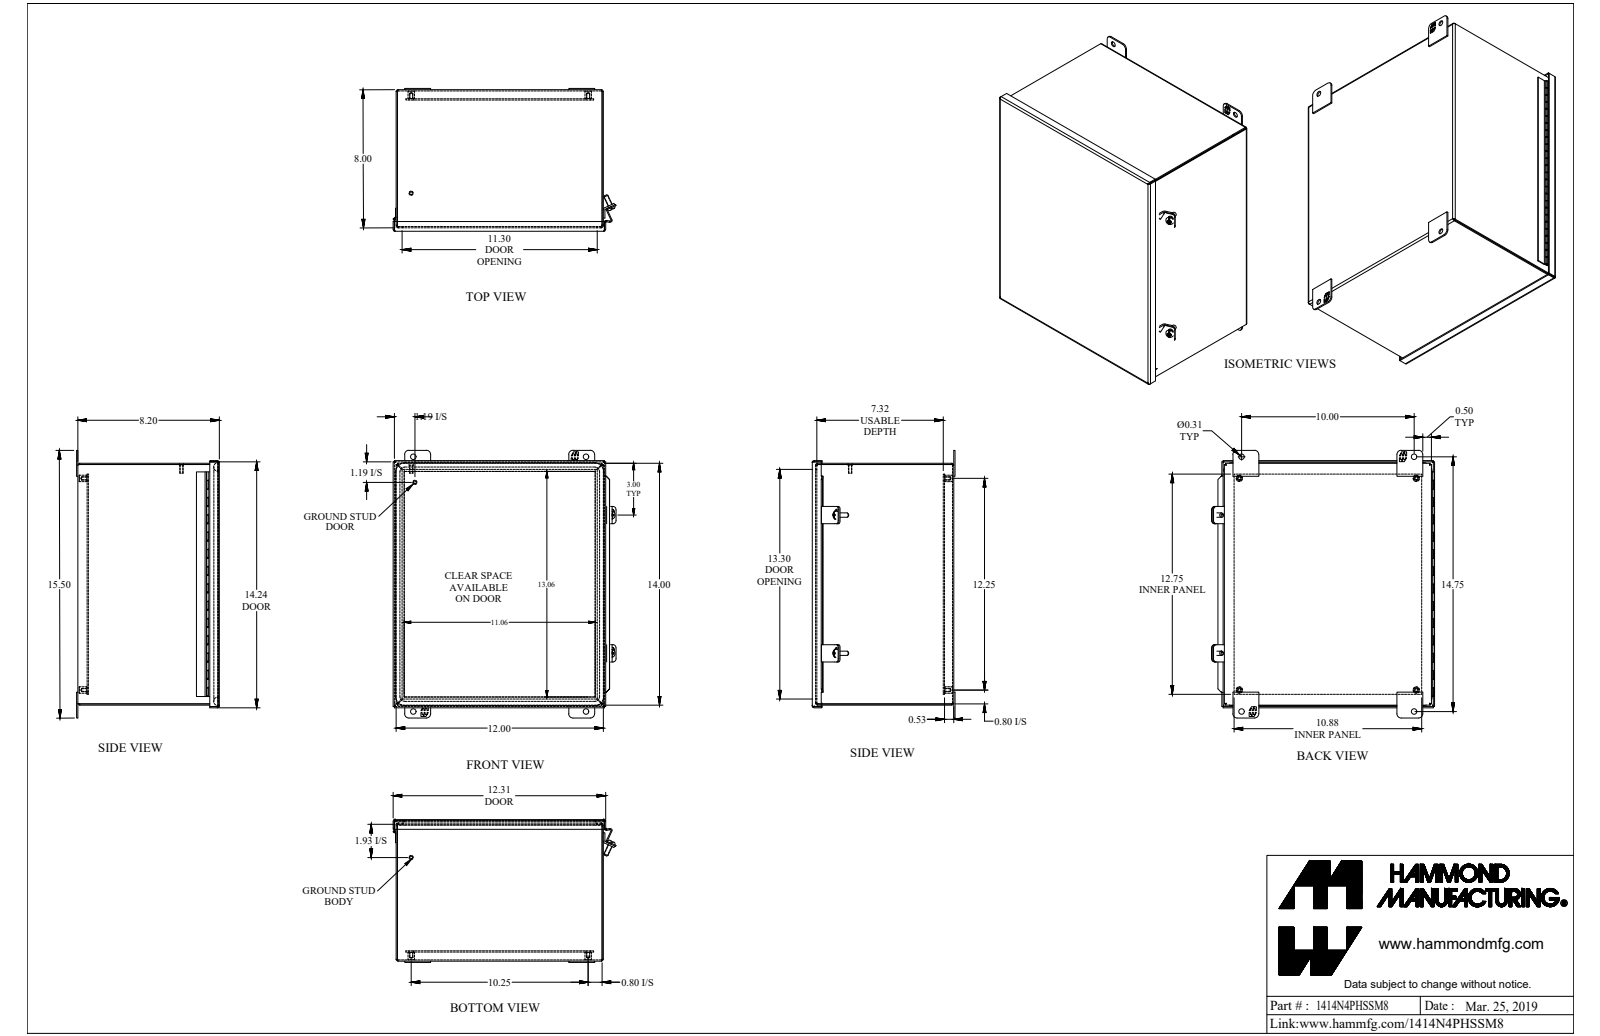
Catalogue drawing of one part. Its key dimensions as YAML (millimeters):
part_name: "1414N4PHSSM8"
step_written_by: "SolidWorks 2018 (AUTOMOTIVE_DESIGN)"
units: millimeters
bodies: {solids: 21, faces: 752, planar: 480, cylindrical: 208, other: 64}
overall_size: [393.7, 327.7, 210]
volume: 1207000
surface_area: 1332000
round_holes:
  - {diameter: 4, count: 4}
  - {diameter: 6.7, count: 4}
  - {diameter: 8, count: 4}
  - {diameter: 5.4, count: 2}
  - {diameter: 1.3, count: 1}
round_bosses_or_shafts:
  - {diameter: 9.5, count: 4}
  - {diameter: 6.4, count: 4}
  - {diameter: 12.2, count: 2}
  - {diameter: 4.8, count: 2}
  - {diameter: 2.5, count: 1}
  - {diameter: 1.1, count: 1}
partial_cylinders:
  - {radius: 6.4, count: 24}
  - {radius: 0.9, count: 9}
  - {radius: 2.7, count: 9}
  - {radius: 4.8, count: 8}
  - {radius: 0.2, count: 4}
  - {radius: 1.2, count: 4}
  - {radius: 2, count: 4}
  - {radius: 3, count: 4}
face_to_face_distances: [1.8, 206.4, 192.9, 13.5, 303, 353.8, 208.2, 204.5, 15.3, 194.7]
hole_center_spacings: [259.1, 405.7, 31.9, 342.9, 428.6, 260.4, 260.4, 311.2]
